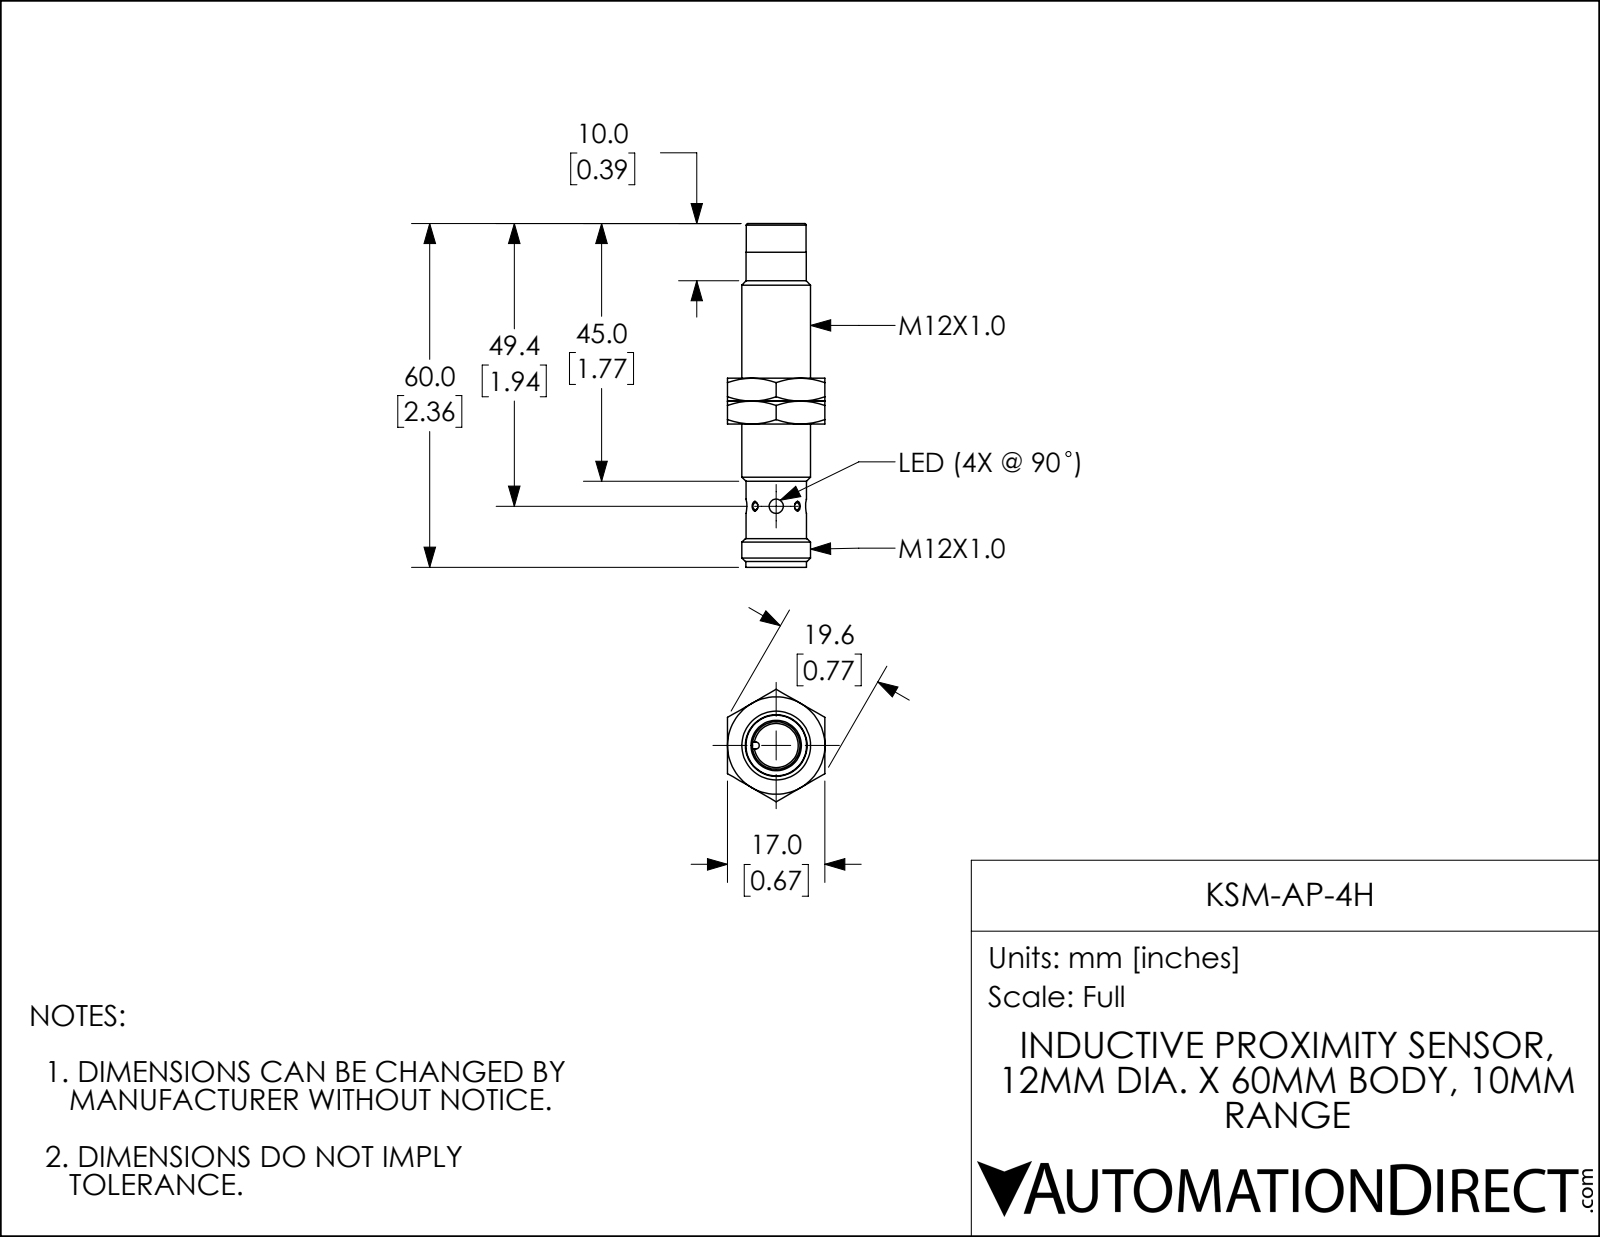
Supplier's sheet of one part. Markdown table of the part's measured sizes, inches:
| quantity | value |
| --- | --- |
| part name | KSM-AP-4H |
| STEP written by | SolidWorks 2017 (AUTOMOTIVE_DESIGN) |
| units | inches |
| bodies | 3 solids, 86 faces (25 planar, 14 cylindrical, 47 other) |
| overall size | 2.362 × 0.773 × 0.669 |
| volume | 0.423 in³ |
| surface area | 6.073 in² |
| round holes (diameter × count) | 0.098 × 2, 0.327 × 1, 0.43 × 1 |
| round bosses / shafts (diameter × count) | 0.472 × 1, 0.417 × 1, 0.415 × 1, 0.413 × 1, 0.411 × 1 |
| partial cylindrical surfaces (radius × count) | 0.024 × 1 |
| main face-to-face distances | 0.157, 0.669, 0.315, 1.378, 1.22, 1.063, 0.634, 0.791, 0.949, 2.012 |
